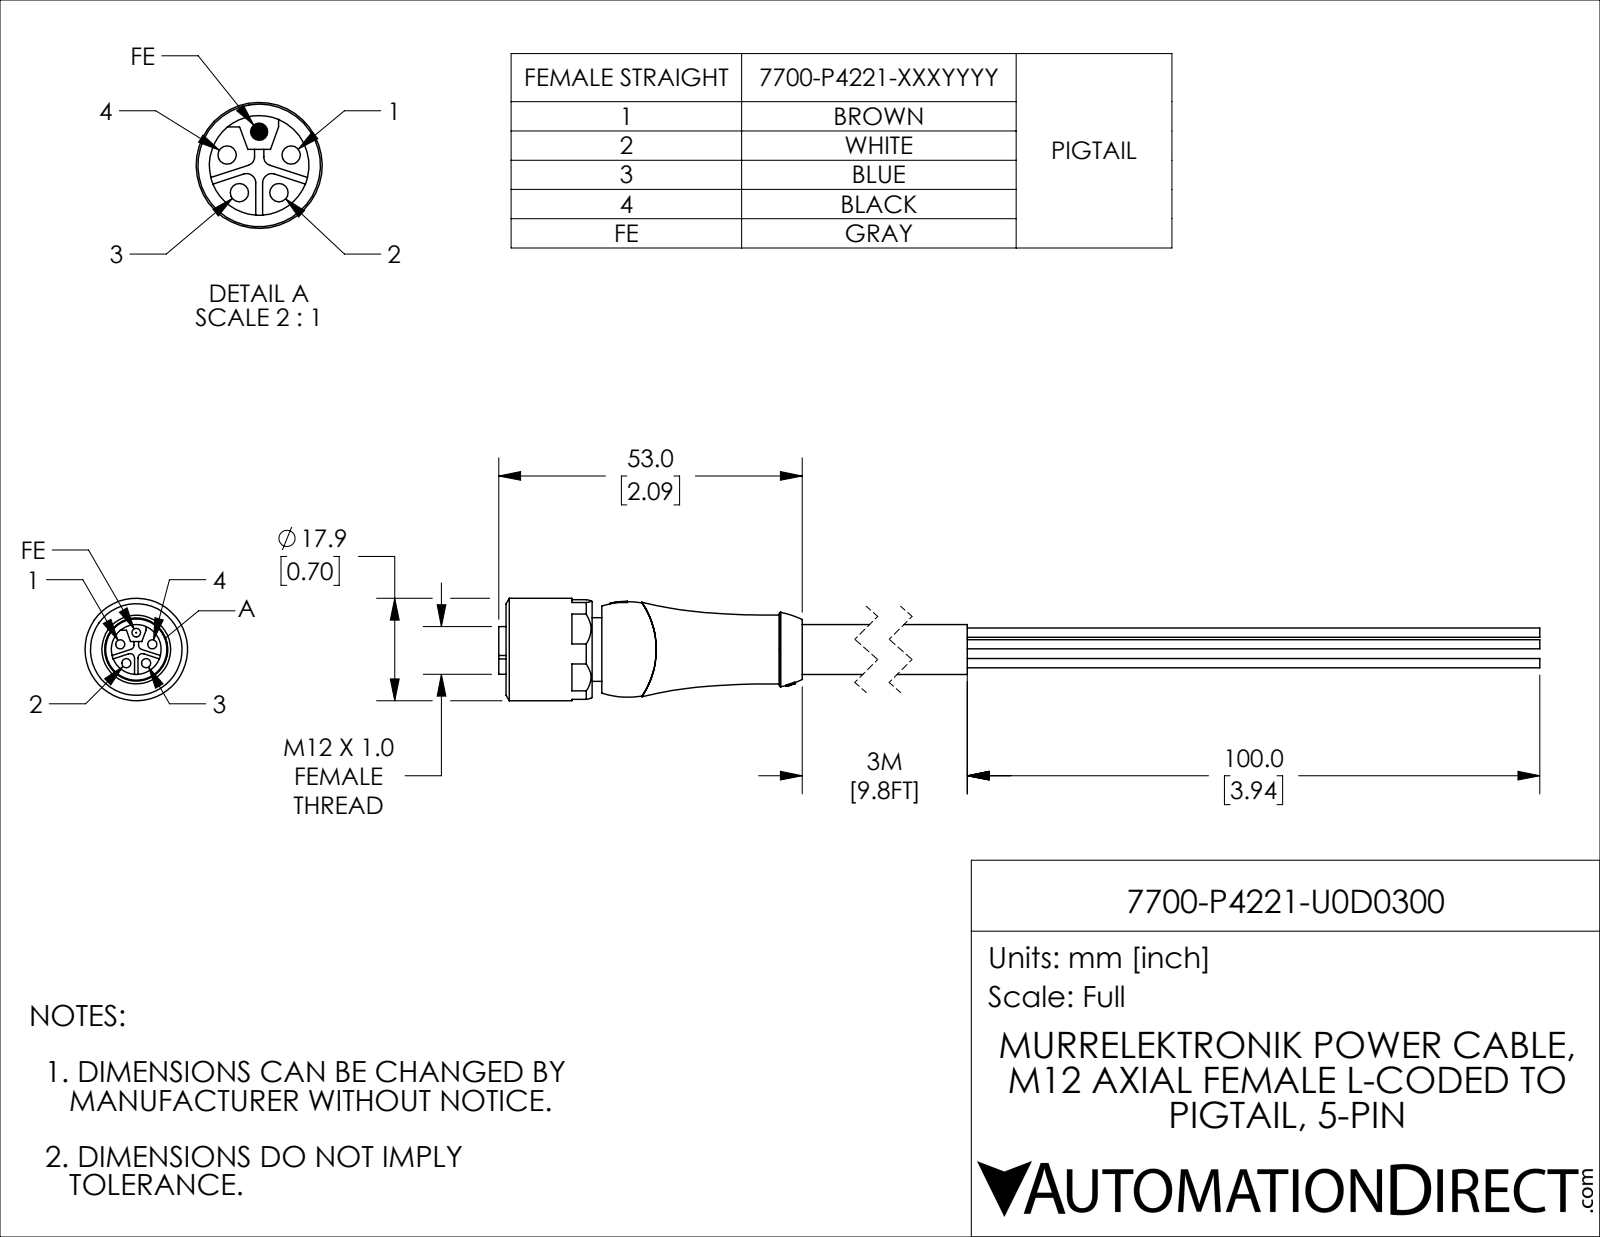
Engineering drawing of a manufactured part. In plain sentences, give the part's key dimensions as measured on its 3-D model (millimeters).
The part is named "7700-P4221-U0D0300". Its 3-D file was written by "SolidWorks 2021 (CONFIG_CONTROL_DESIGN)". It is 2 solids with 142 faces: 69 planar, 40 cylindrical and 33 other. Overall it measures 193 by 17.9 by 17.9 millimeters. Its volume is 12 000 cubic millimeters and its surface area 8 277 square millimeters. Round holes: 4 of diameter 1.6, 1 of diameter 11, 1 of diameter 13. Round bosses or shafts: 1 of diameter 17.9, 1 of diameter 13, 1 of diameter 11.1, 1 of diameter 8.7, 1 of diameter 1.6, 1 of diameter 1.5. Partial cylindrical surfaces (rounded edges, fillets, slot ends): 4 of radius 0.8. The main face-to-face distances are 16.7, 15, 1.7, 16.9, 91.7, 76.7, 75, 4.6, 9.2, 5.8. The hole center spacings are 2.9, 3.5, 5.6.
